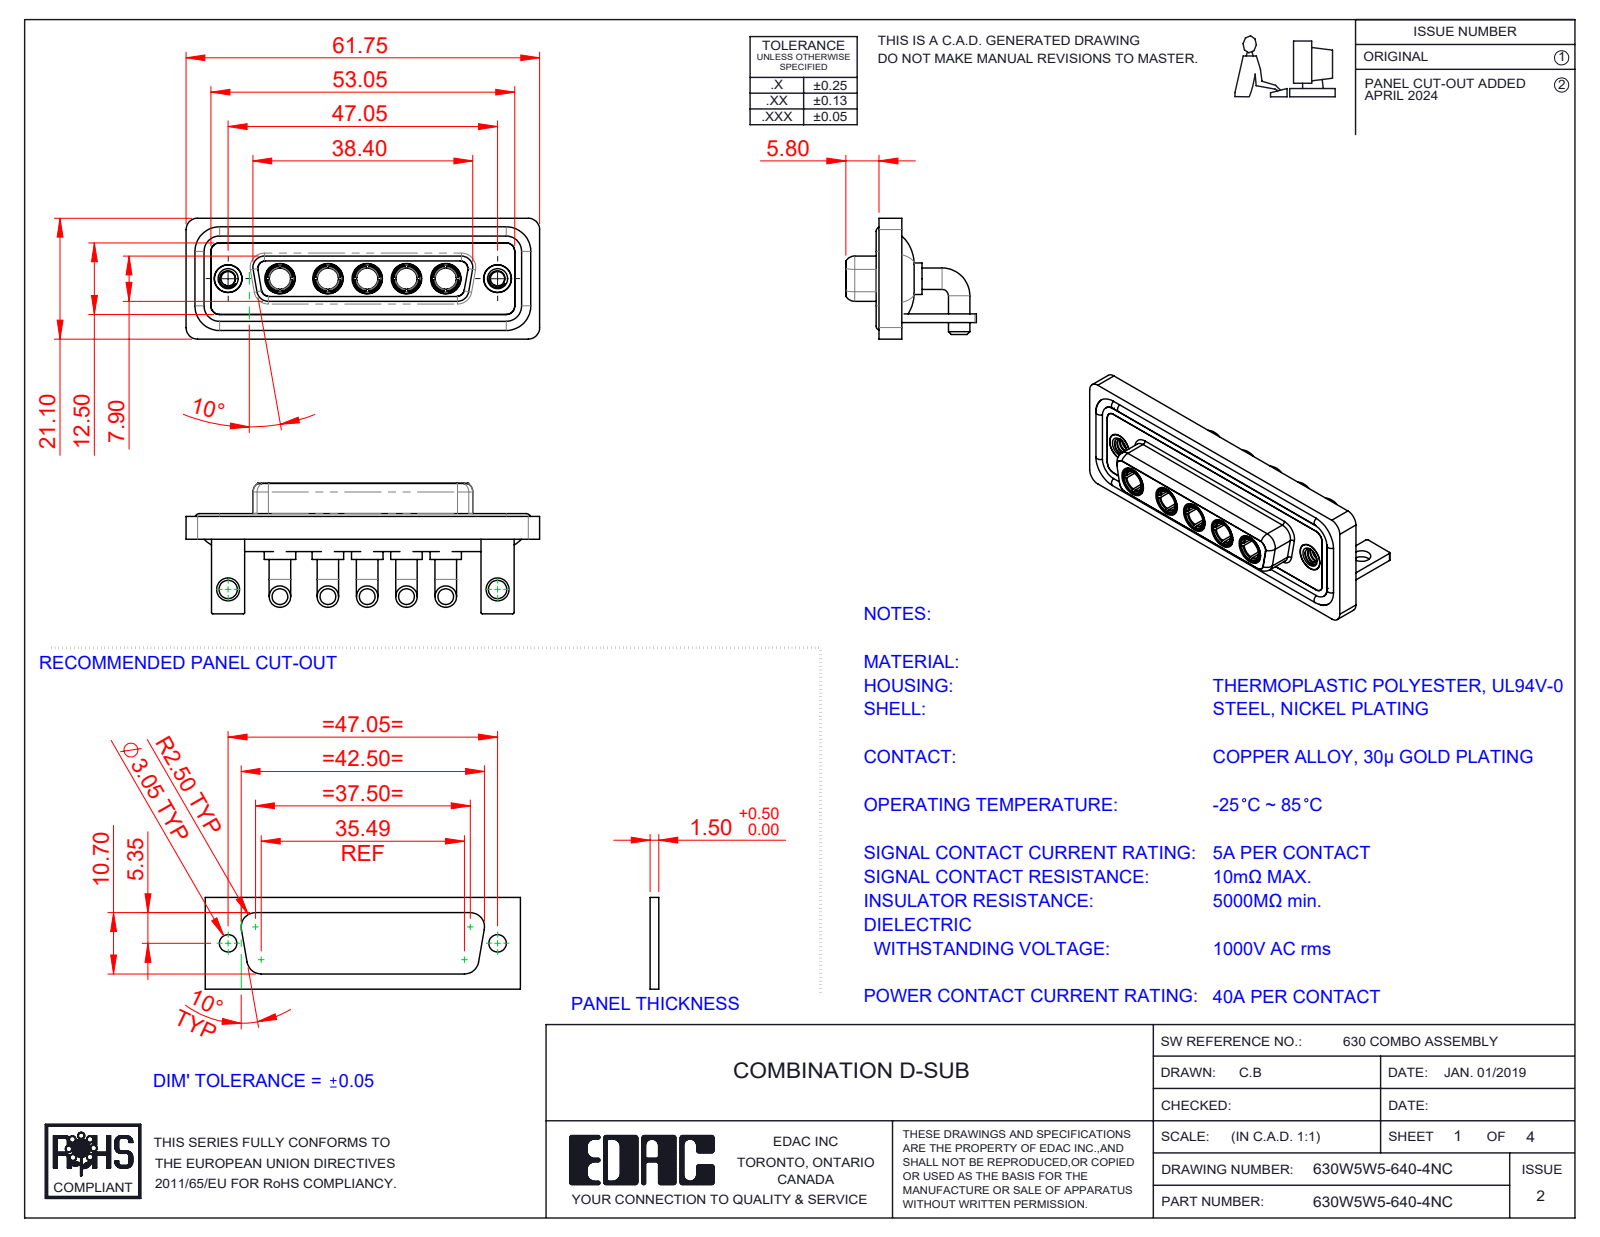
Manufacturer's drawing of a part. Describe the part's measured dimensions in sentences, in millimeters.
The part is named "630Combo Waterproof Housing_25 Contacts; 630Combo Stabilizer Bracket_50 Contacts; 630Combo Shell Front_25 Contacts; 630Combo Housing_5W5 (+4 more)". Its 3-D file was written by "SolidWorks 2023 (CONFIG_CONTROL_DESIGN)". It is 19 solids with 818 faces: 270 planar, 335 cylindrical and 213 other. Overall it measures 61.75 by 22.8 by 21.1 millimeters. Its volume is 9 158 cubic millimeters and its surface area 14 771 square millimeters. Round holes: 7 of diameter 4.85, 5 of diameter 3.7, 5 of diameter 5.3, 2 of diameter 2.5, 2 of diameter 3.2, 2 of diameter 4, 2 of diameter 4.05, 2 of diameter 5. Round bosses or shafts: 10 of diameter 3.75, 5 of diameter 5.5, 5 of diameter 5.2, 5 of diameter 4.96, 5 of diameter 4.75, 4 of diameter 1.6, 2 of diameter 4.95, 2 of diameter 4.8. Partial cylindrical surfaces (rounded edges, fillets, slot ends): 19 of radius 2, 18 of radius 1.5, 16 of radius 0.25, 8 of radius 1.35, 8 of radius 1.6, 5 of radius 0.5, 5 of radius 2.1, 4 of radius 0.6. The main face-to-face distances are 0.4, 1.8, 2.9, 3.7, 1.5, 4.1, 1.1, 1.4, 1.6, 2.5. The hole center spacings are 6.86, 9.04, 38.01, 47.05, 6.87, 8.38, 13.72, 13.73.
